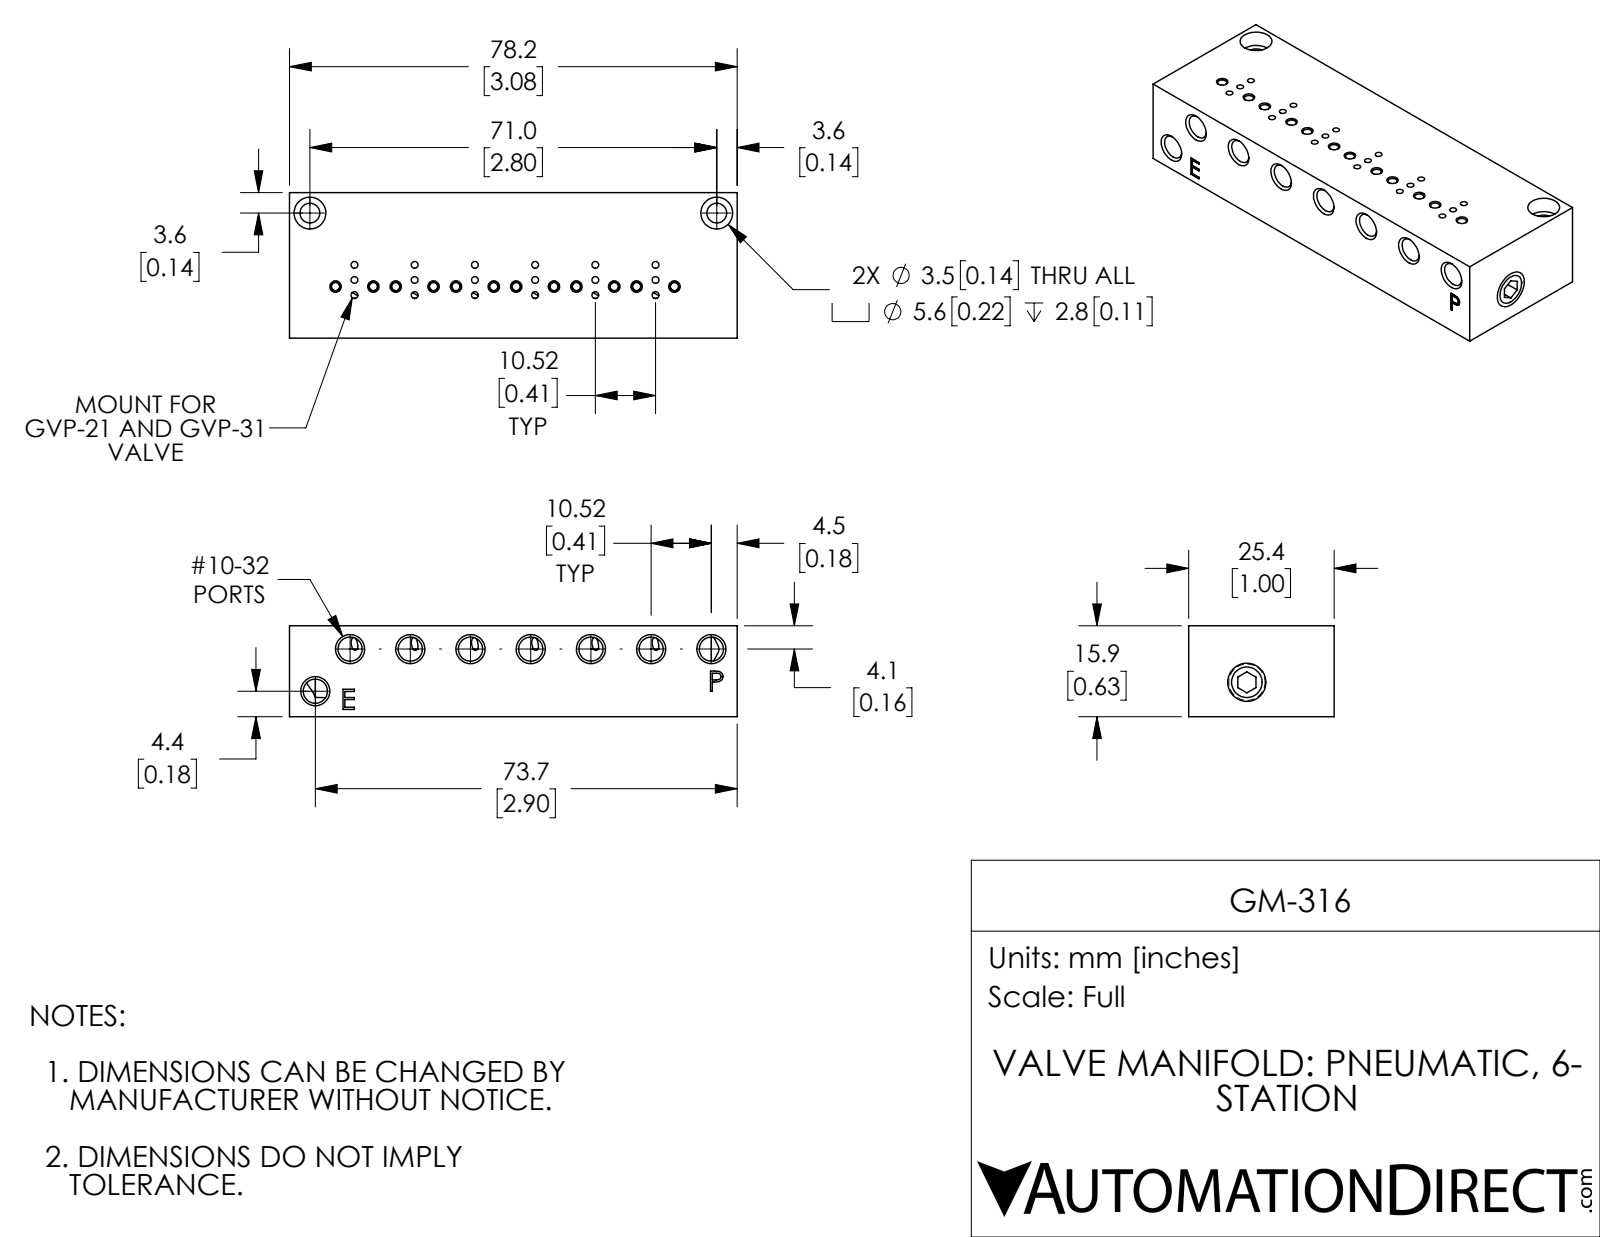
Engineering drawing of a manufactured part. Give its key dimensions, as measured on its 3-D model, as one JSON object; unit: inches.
{"part_name": "GM-316", "step_written_by": "SolidWorks 2018 (AUTOMOTIVE_DESIGN)", "units": "inches", "bodies": {"solids": 3, "faces": 283, "planar": 61, "cylindrical": 116, "other": 106}, "overall_size": [3.077, 1, 0.625], "volume_in3": 1.639, "surface_area_in2": 18.48, "round_holes": [[0.047, 18], [0.063, 12], [0.055, 10], [0.166, 8], [0.055, 2], [0.136, 2], [0.213, 2], [0.219, 2]], "round_bosses_or_shafts": [[0.25, 2]], "face_to_face_distances": [0.625, 1, 3.077, 0.125, 0.513, 0.112, 0.25, 2.827, 0.125, 2.577], "hole_center_spacings": [0.828, 0.414, 0.835, 0.104, 0.414, 0.427, 1.242, 0.198]}
